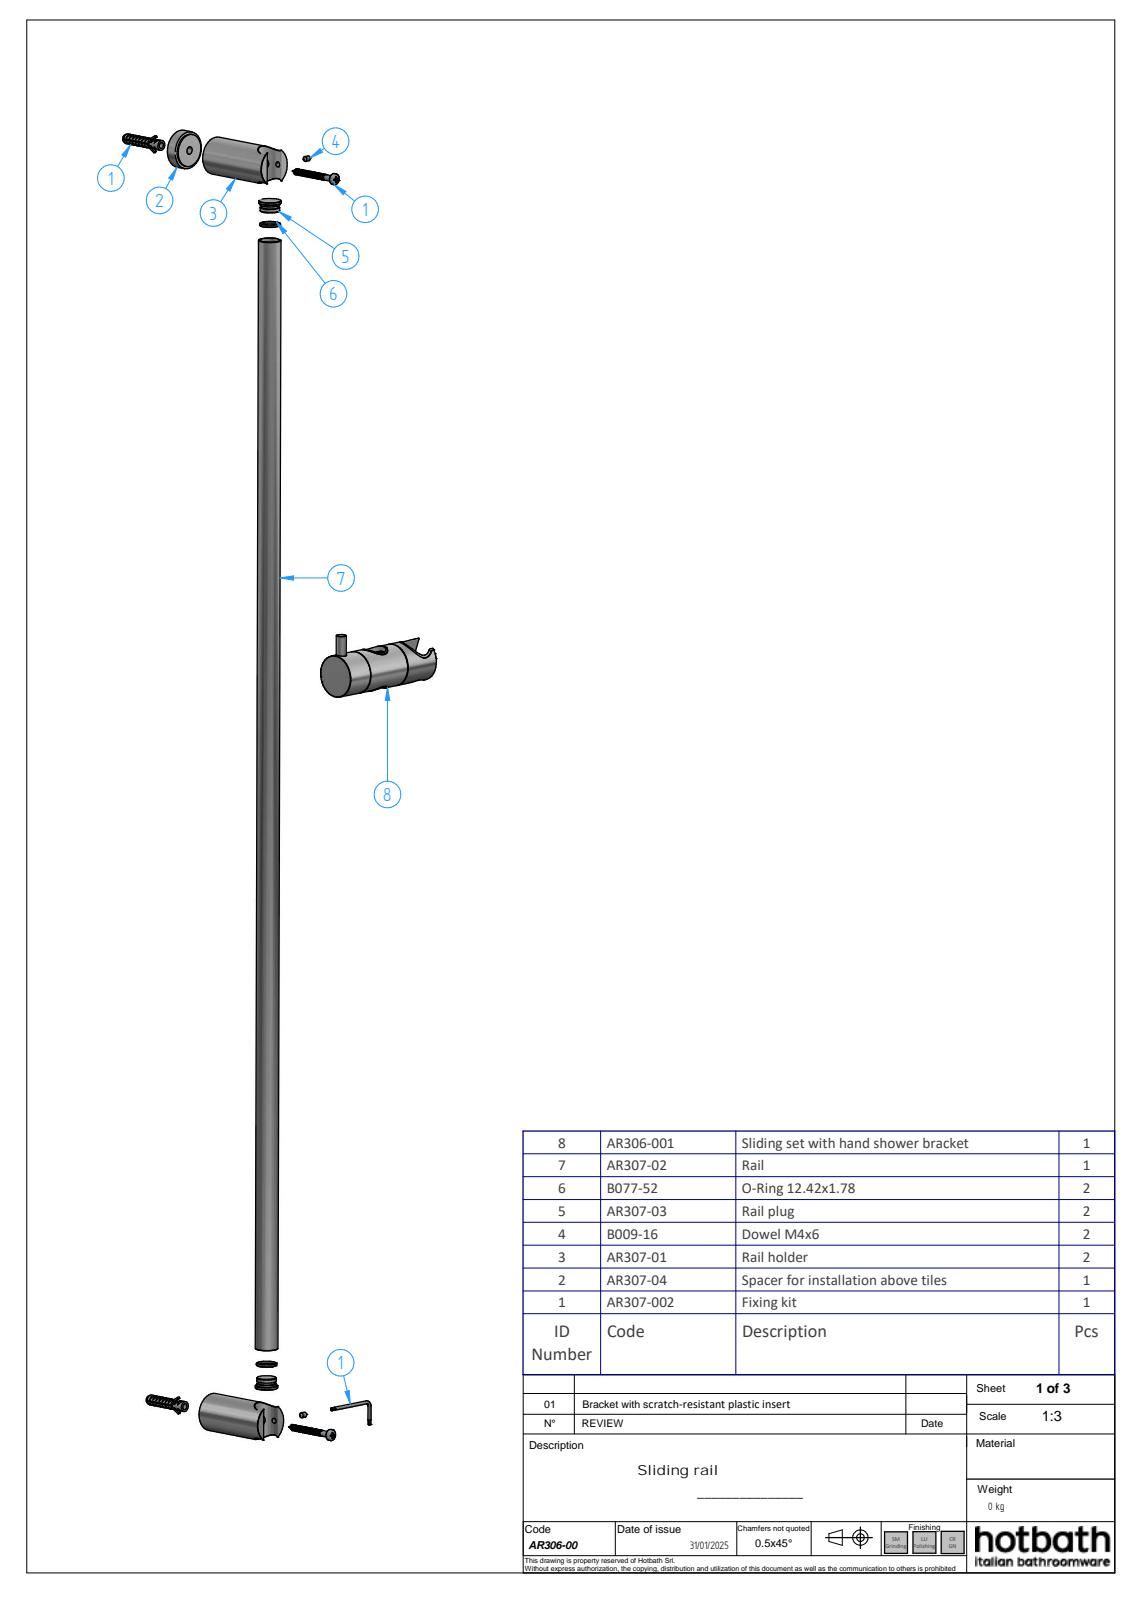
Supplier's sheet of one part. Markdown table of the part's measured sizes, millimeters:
| quantity | value |
| --- | --- |
| part name | AR306-00 Rel1; AR307-01; AR307-02; B009-16 (+8 more) |
| STEP written by | Solid Edge (AUTOMOTIVE_DESIGN) |
| units | millimeters |
| bodies | 14 solids, 487 faces (150 planar, 193 cylindrical, 144 other) |
| overall size | 904 × 98.5 × 76.95 |
| volume | 152 193 mm³ |
| surface area | 145 730 mm² |
| round holes (diameter × count) | 4.13 × 2, 6 × 2, 8 × 2, 12 × 2, 26 × 2, 4.5 × 1, 4.92 × 1, 8.1 × 1, 13.8 × 1, 15.2 × 1, 16 × 1, 16.3 × 1 |
| round bosses / shafts (diameter × count) | 30 × 2, 4 × 2, 33.5 × 1, 30.8 × 1, 21.1 × 1, 20 × 1, 19 × 1, 18 × 1 |
| partial cylindrical surfaces (radius × count) | 0.5 × 12, 1.25 × 12, 1.5 × 12, 2 × 10, 0.2 × 8, 1 × 2, 13 × 2, 5.1 × 1 |
| main face-to-face distances | 2.7, 1.5, 8.5, 67.6, 64.9, 63.5, 6.5, 1.4, 57.4, 54.7 |
| hole center spacings | 820, 9.99, 37.8, 281.89, 291.26, 528.74, 538.14 |
